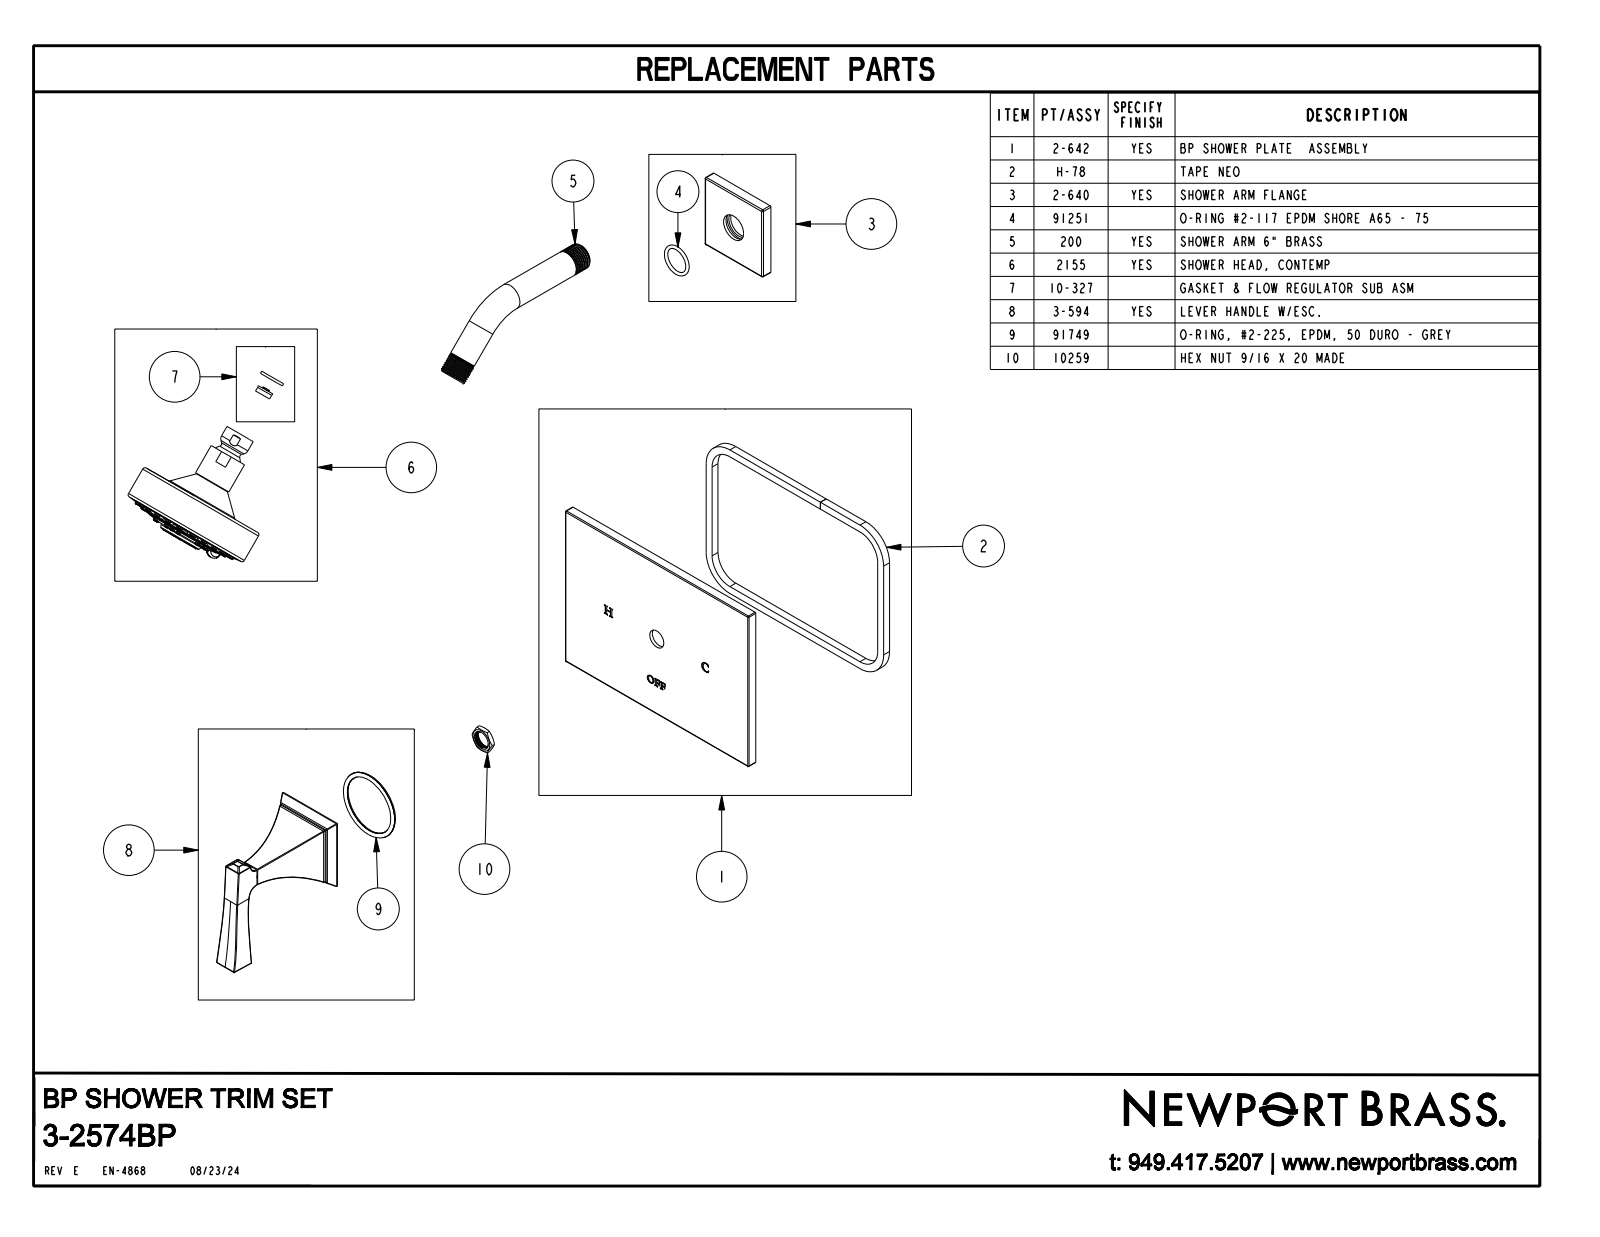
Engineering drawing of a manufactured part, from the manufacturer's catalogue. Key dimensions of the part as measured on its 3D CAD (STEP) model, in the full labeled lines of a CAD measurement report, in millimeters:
Part name (STEP PRODUCT): 3-2574BP
STEP written by: CREO PARAMETRIC BY PTC INC, 2018400 (CONFIG_CONTROL_DESIGN)
Units: millimetres
Bodies: 2 solids, 1435 faces (195 planar, 230 cylindrical, 1010 other)
Overall size (bounding box): 413.4 × 207.6 × 196.9
Volume: 652 000 mm³ · Surface area: 121 500 mm²
Round holes (diameter × count): ⌀1.5 ×8, ⌀23.5 ×1
Round bosses / shafts (diameter × count): ⌀3.6 ×39, ⌀4.2 ×23, ⌀20.7 ×2, ⌀101.6 ×1, ⌀94.6 ×1, ⌀59 ×1, ⌀29.2 ×1, ⌀23 ×1
Partial cylindrical surfaces — rounded edges, fillets, slot ends (radius × count): R0.5 ×16, R0.8 ×8, R1 ×8, R1.5 ×8, R2 ×8, R0.5 ×2, R3.5 ×1, R12 ×1
Main face-to-face distances: 7.9, 8.9, 1, 139.7, 196.9, 67.3, 129.5, 91.3, 105.5, 24
Hole centre spacings: 11.3, 14.7, 20.8, 20.8, 27.2, 11.3, 14.7, 27.2
